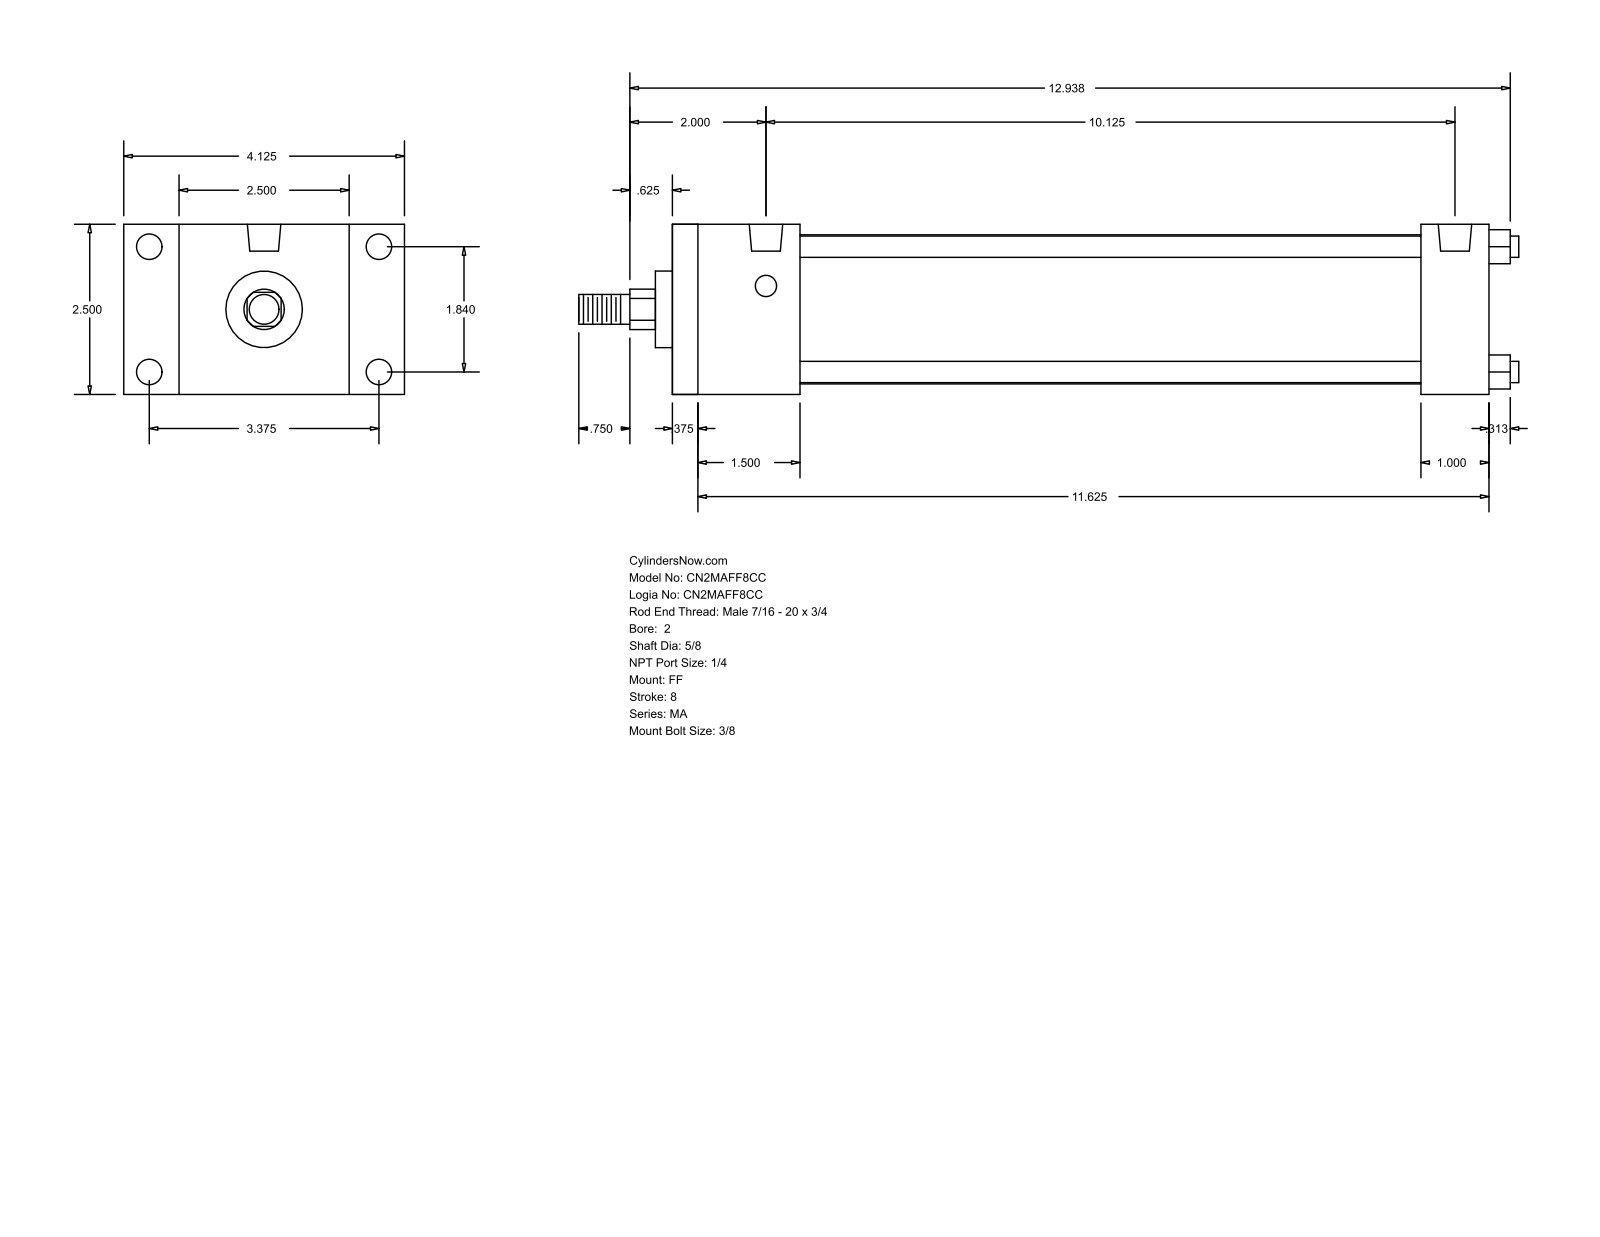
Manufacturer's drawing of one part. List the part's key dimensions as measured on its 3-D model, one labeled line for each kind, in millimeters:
Part name (STEP PRODUCT): MA_FF__0200_0.625
STEP written by: GSSL Pune (CONFIG_CONTROL_DESIGN)
Units: millimetres
Bodies: 0 solids, 92 faces (64 planar, 28 cylindrical, 0 other)
Overall size (bounding box): 350.84 × 104.78 × 63.5
Round holes (diameter × count): ⌀7.94 ×4, ⌀9.53 ×4, ⌀12.49 ×2
Round bosses / shafts (diameter × count): ⌀7.94 ×4, ⌀55.63 ×1, ⌀28.57 ×1, ⌀15.88 ×1, ⌀11.11 ×1
Partial cylindrical surfaces — rounded edges, fillets, slot ends (radius × count): R7.54 ×1
Main face-to-face distances: 63.5, 304.8, 9.52, 295.28, 38.1, 47.62, 279.39, 269.87, 231.77, 257.18
Hole centre spacings: 46.74, 85.72, 97.63, 257.18
